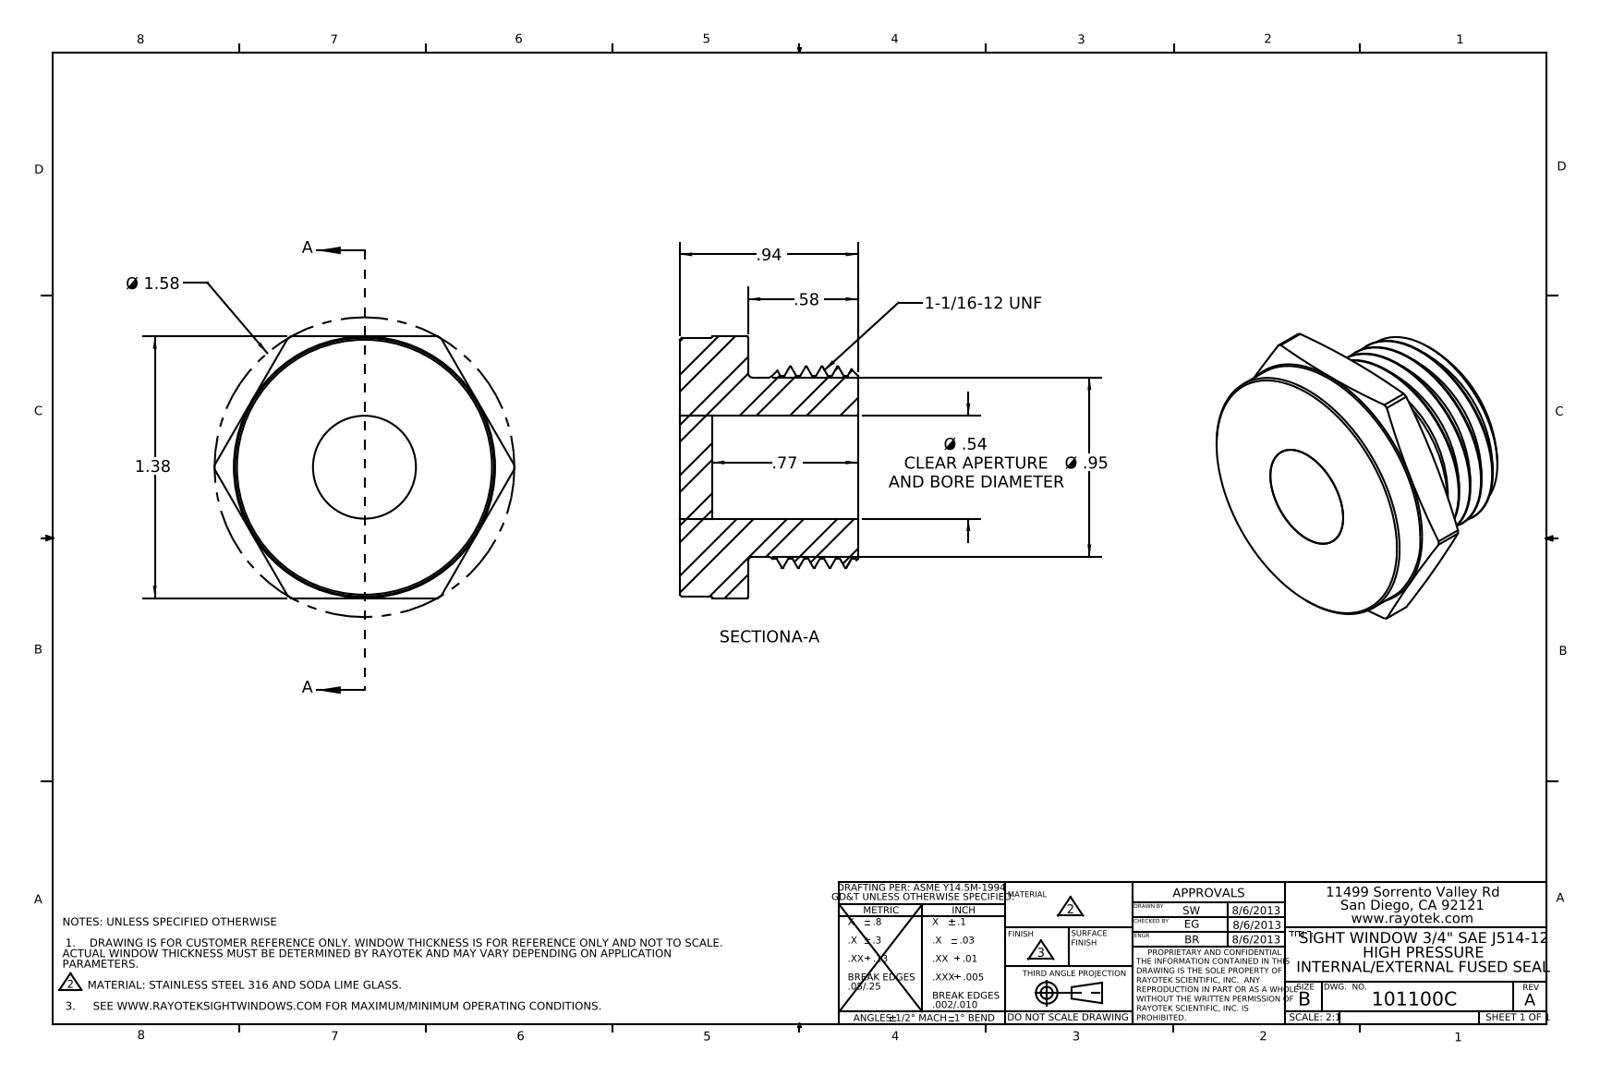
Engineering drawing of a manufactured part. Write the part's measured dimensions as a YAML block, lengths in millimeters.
part_name: "403100"
step_written_by: "SolidWorks 2012 (AUTOMOTIVE_DESIGN)"
units: millimeters
bodies: {solids: 2, faces: 56, planar: 11, cylindrical: 24, other: 21}
overall_size: [40.2, 35.1, 23.9]
volume: 13600
surface_area: 6096
round_holes:
  - {diameter: 13.8, count: 1}
round_bosses_or_shafts:
  - {diameter: 34.7, count: 1}
  - {diameter: 27, count: 1}
  - {diameter: 24, count: 1}
partial_cylinders:
  - {radius: 20.1, count: 1}
face_to_face_distances: [9.1, 14.7, 23.9, 35.1, 19.6, 4.8, 4.3]
